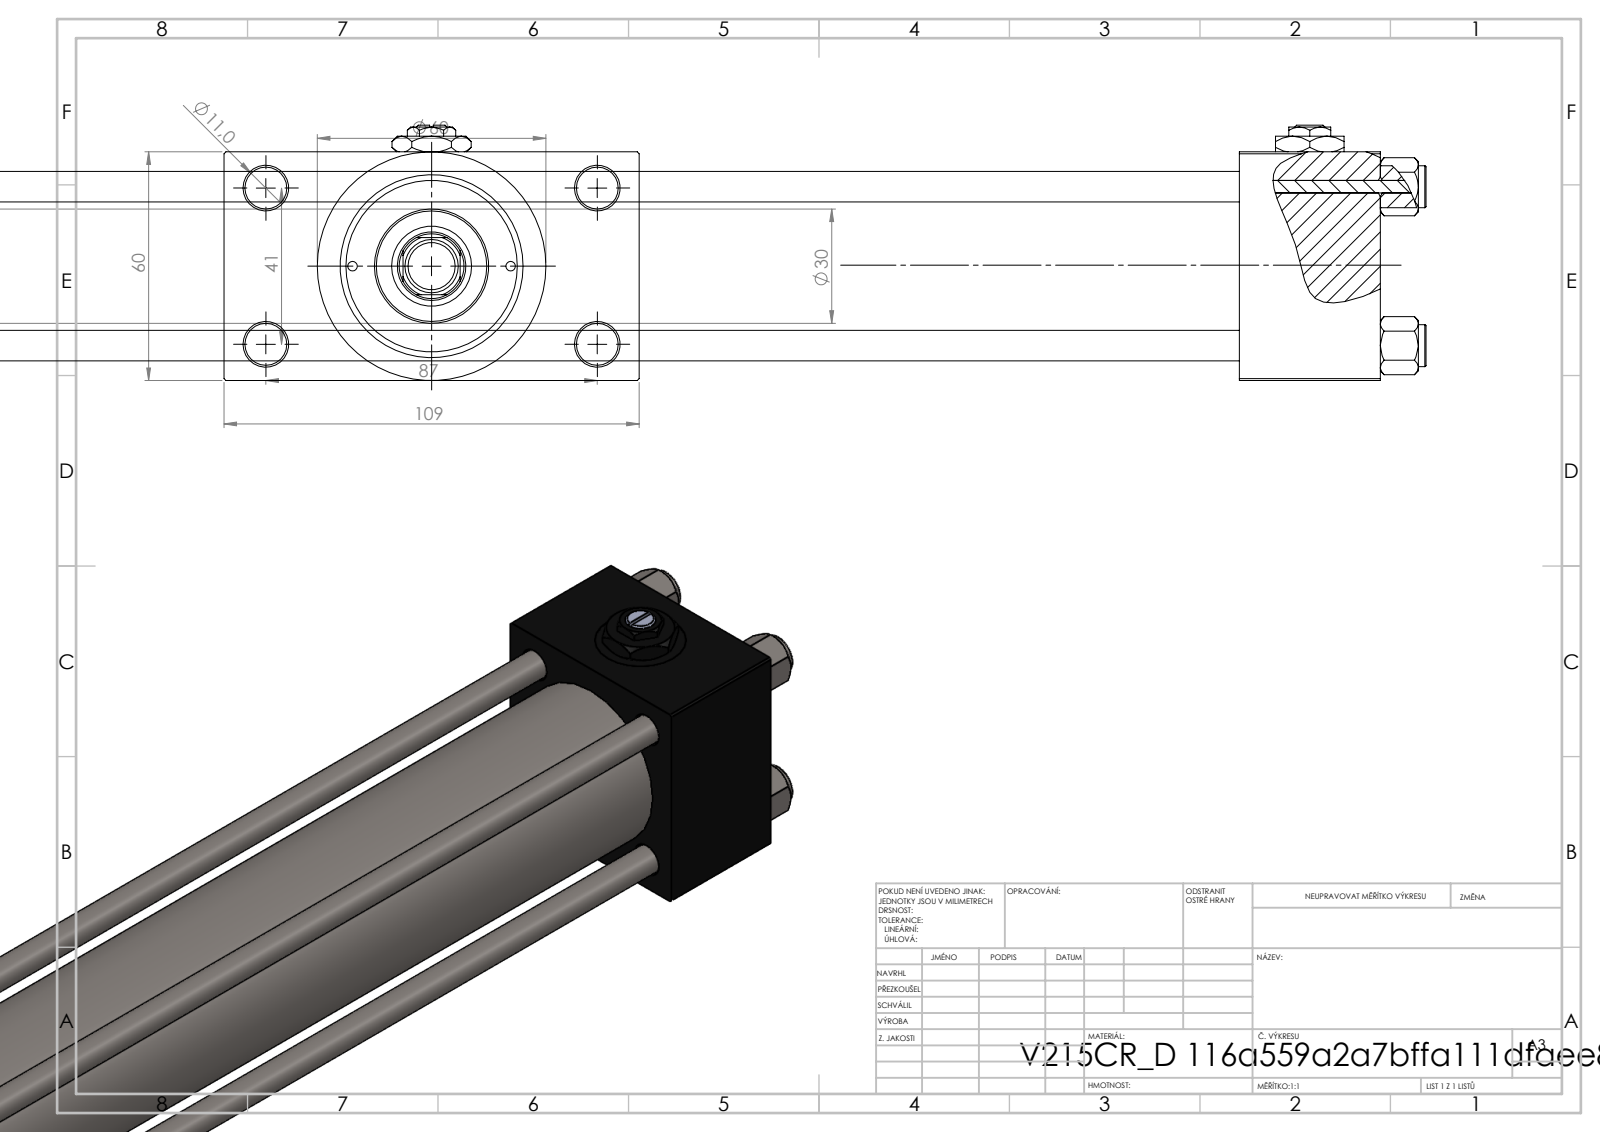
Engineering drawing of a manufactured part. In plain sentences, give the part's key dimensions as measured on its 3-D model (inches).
The part is named "ROD_END_AH; V215CR_D_Body; V215CR_D_TYCINKA; Zatka_pro_OIL_PORT (+3 more)". Its 3-D file was written by "SolidWorks 2019 (CONFIG_CONTROL_DESIGN)". It is 14 solids with 1228 faces: 552 planar, 108 cylindrical and 568 other. Overall it measures 22.953 by 4.291 by 2.638 inches. Its volume is 51.57 cubic inches and its surface area 445.4 square inches. Round holes: 4 of diameter 0.315, 4 of diameter 0.433, 2 of diameter 0.098, 2 of diameter 0.276, 2 of diameter 0.656, 2 of diameter 0.945, 1 of diameter 0.335, 1 of diameter 0.709, 1 of diameter 0.827, 1 of diameter 1.22, 1 of diameter 1.575, 1 of diameter 1.772. Round bosses or shafts: 4 of diameter 0.433, 1 of diameter 2.362, 1 of diameter 1.811, 1 of diameter 1.181, 1 of diameter 0.551, 1 of diameter 0.472. Partial cylindrical surfaces (rounded edges, fillets, slot ends): 1 of radius 0.335. The main face-to-face distances are 2.362, 0.965, 3.327, 17.244, 1.457, 18.701, 1.693, 20.394, 18.937, 4.291. The hole center spacings are 0.821, 0.892, 1.161, 1.206, 1.642, 1.832, 1.856, 1.893.
